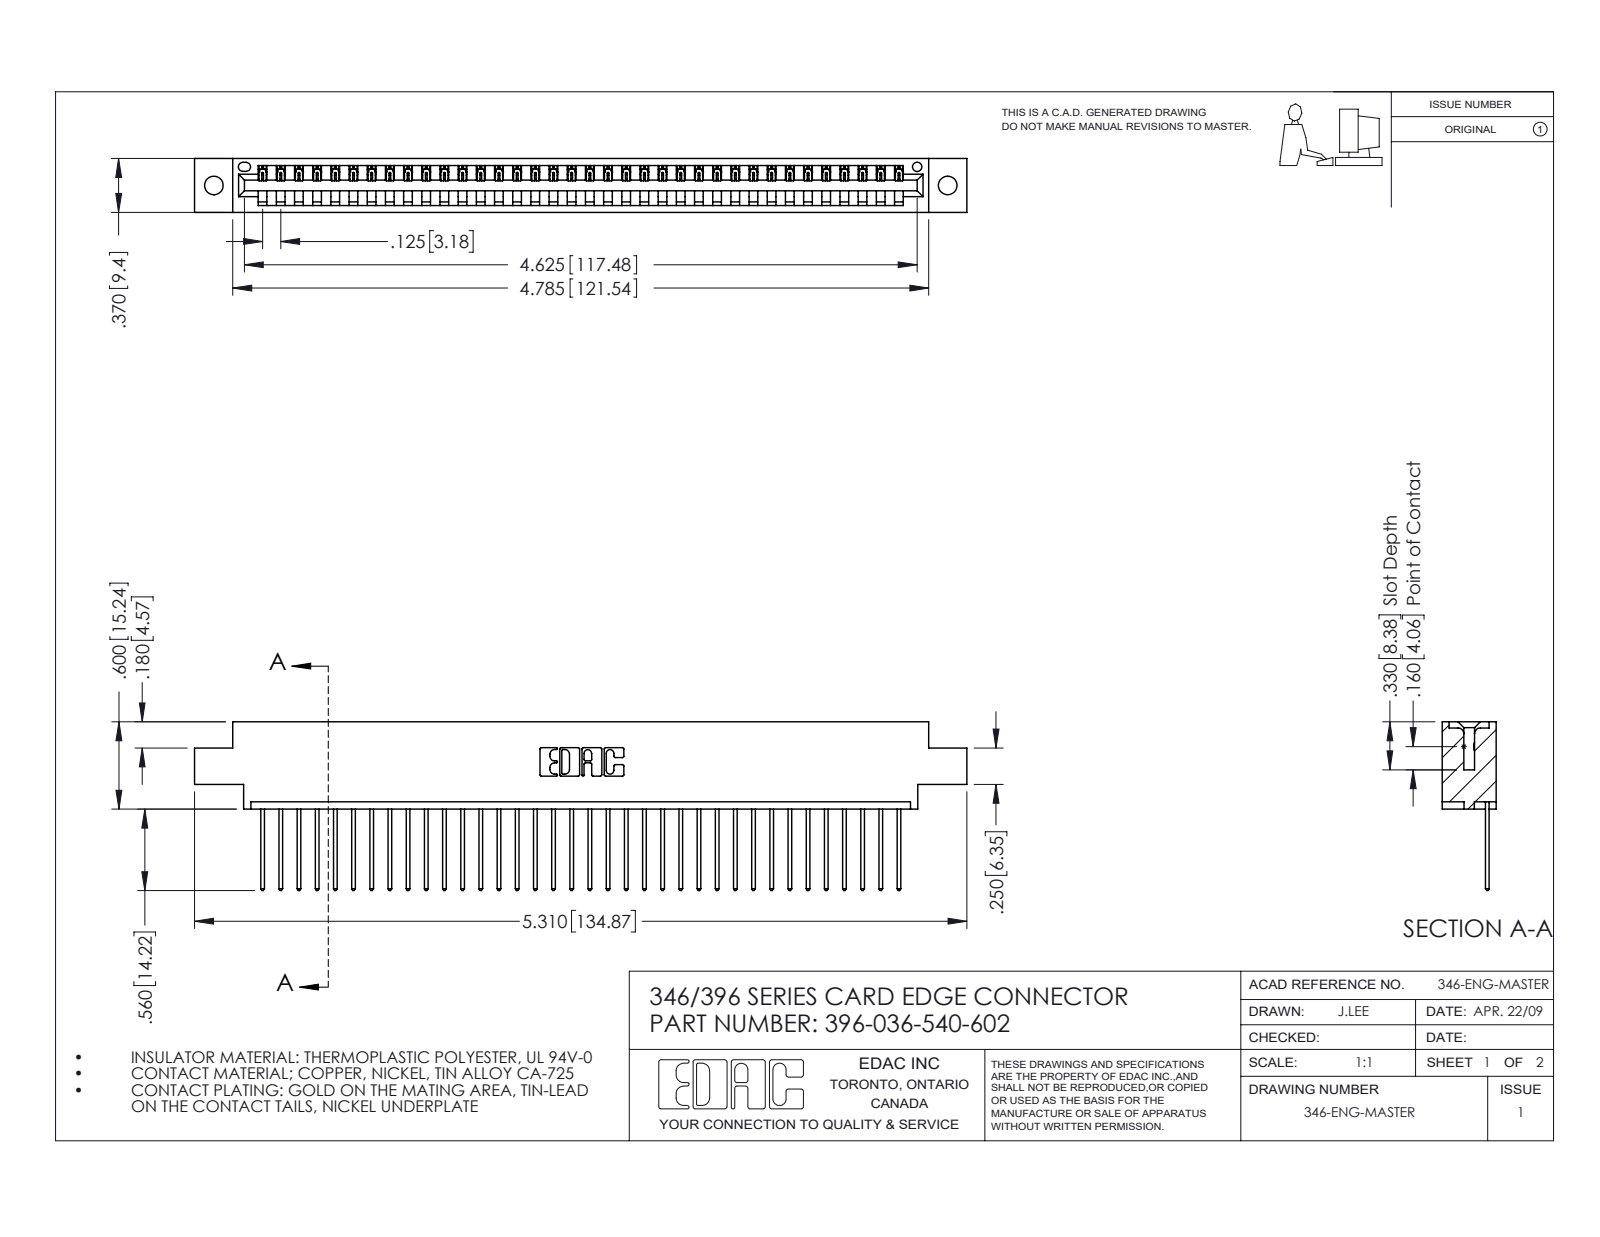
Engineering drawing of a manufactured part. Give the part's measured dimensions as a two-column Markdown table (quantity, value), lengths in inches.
| quantity | value |
| --- | --- |
| part name | 346 Part_0.170 Offset - 0.128 Dia; 396-036-540-602; 345-292-001_345-293-140 |
| STEP written by | SolidWorks 2016 (CONFIG_CONTROL_DESIGN) |
| units | inches |
| bodies | 37 solids, 2214 faces (1520 planar, 694 cylindrical, 0 other) |
| overall size | 5.31 × 1.16 × 0.37 |
| volume | 0.777 in³ |
| surface area | 24.93 in² |
| round holes (diameter × count) | 0.128 × 2, 0.064 × 1 |
| partial cylindrical surfaces (radius × count) | 0.006 × 72, 0.01 × 72, 0.01 × 22, 0.007 × 6, 0.031 × 6, 0.026 × 3, 0.031 × 2, 0.04 × 2 |
| main face-to-face distances | 0.048, 0.322, 0.37, 0.25, 0.072, 0.298, 0.025, 0.148, 0.222, 0.1 |
| hole center spacings | 0.246, 4.836, 5.045 |
